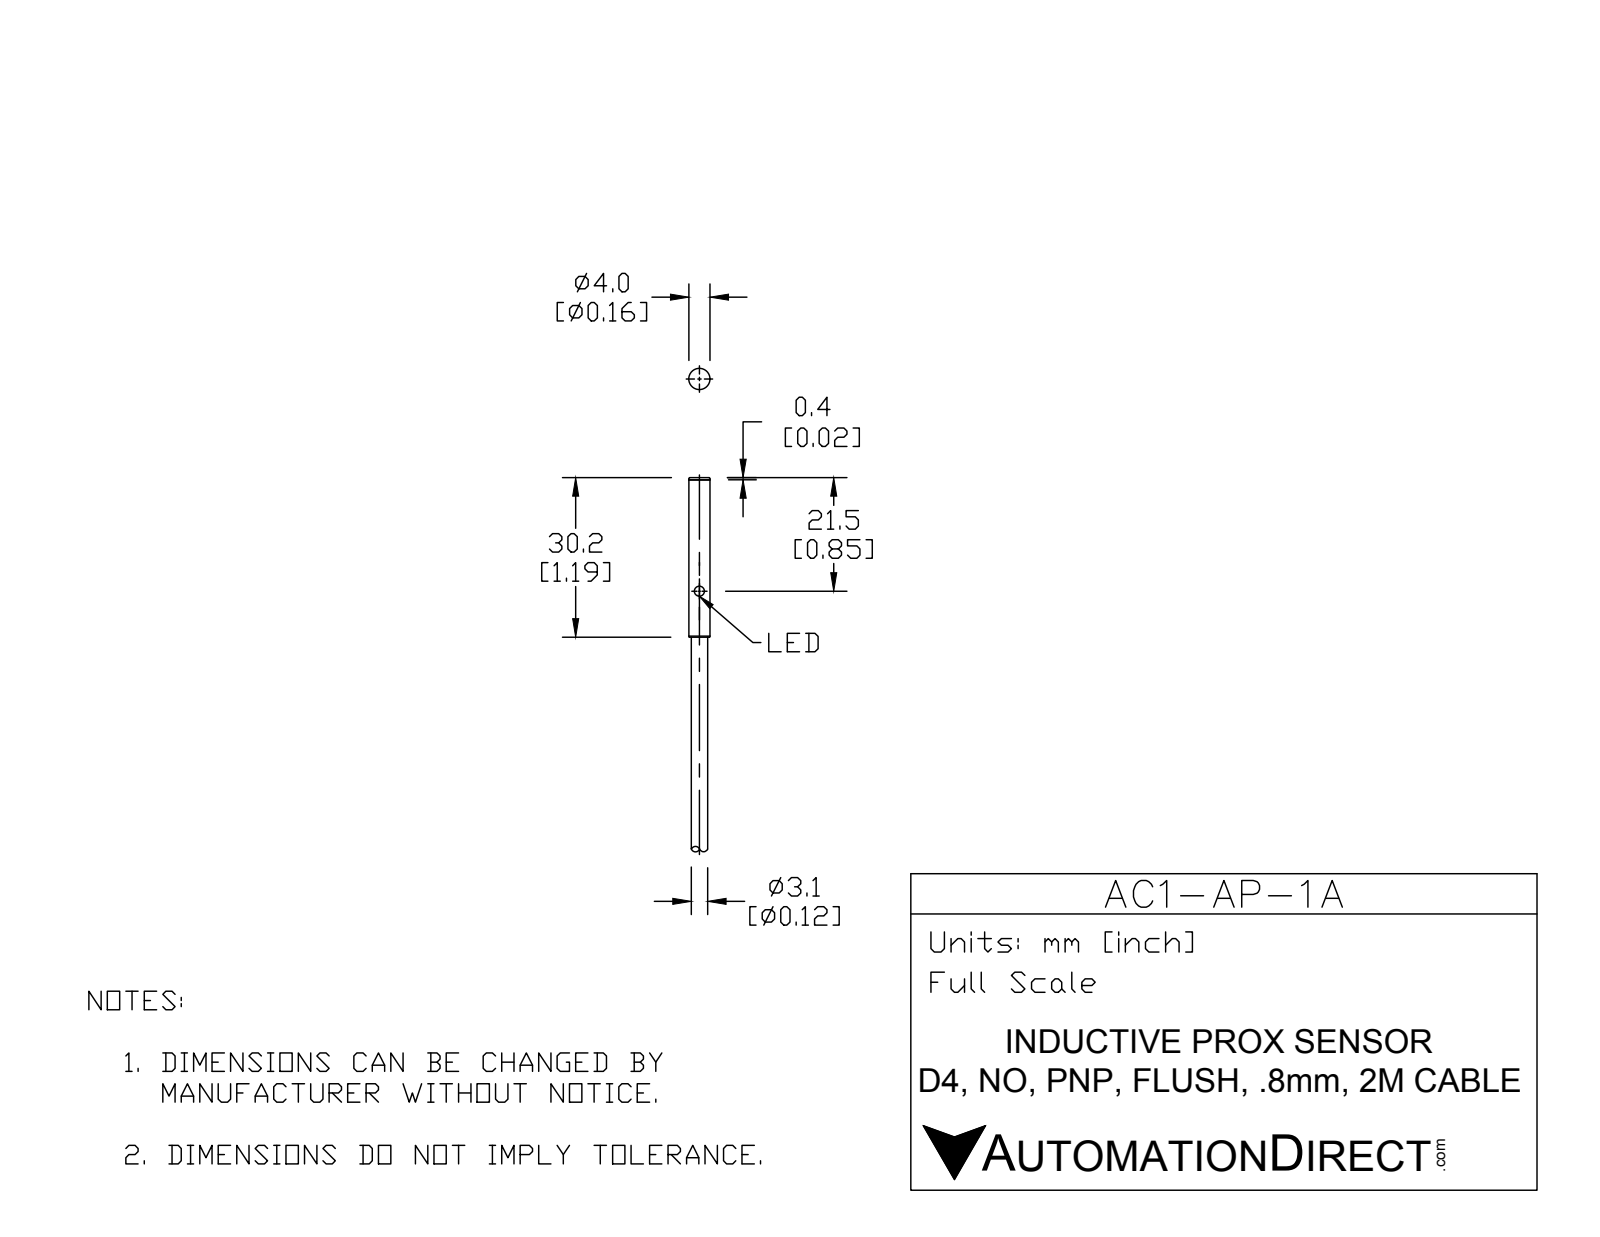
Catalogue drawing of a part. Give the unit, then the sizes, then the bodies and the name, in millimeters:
Units: millimetres
Overall size (bounding box): 80.2 × 4 × 4
Round holes (diameter × count): ⌀1.9 ×1
Round bosses / shafts (diameter × count): ⌀4 ×1, ⌀3.1 ×1
Main face-to-face distances: 30.2, 50, 80.2, 79.8, 29.8, 0.4
Volume: 756 mm³ · Surface area: 905 mm²
Bodies: 2 solids, 20 faces (6 planar, 8 cylindrical, 6 other)
Part name (STEP PRODUCT): AC1-AP-1A
STEP written by: SolidWorks 2015 (CONFIG_CONTROL_DESIGN)
